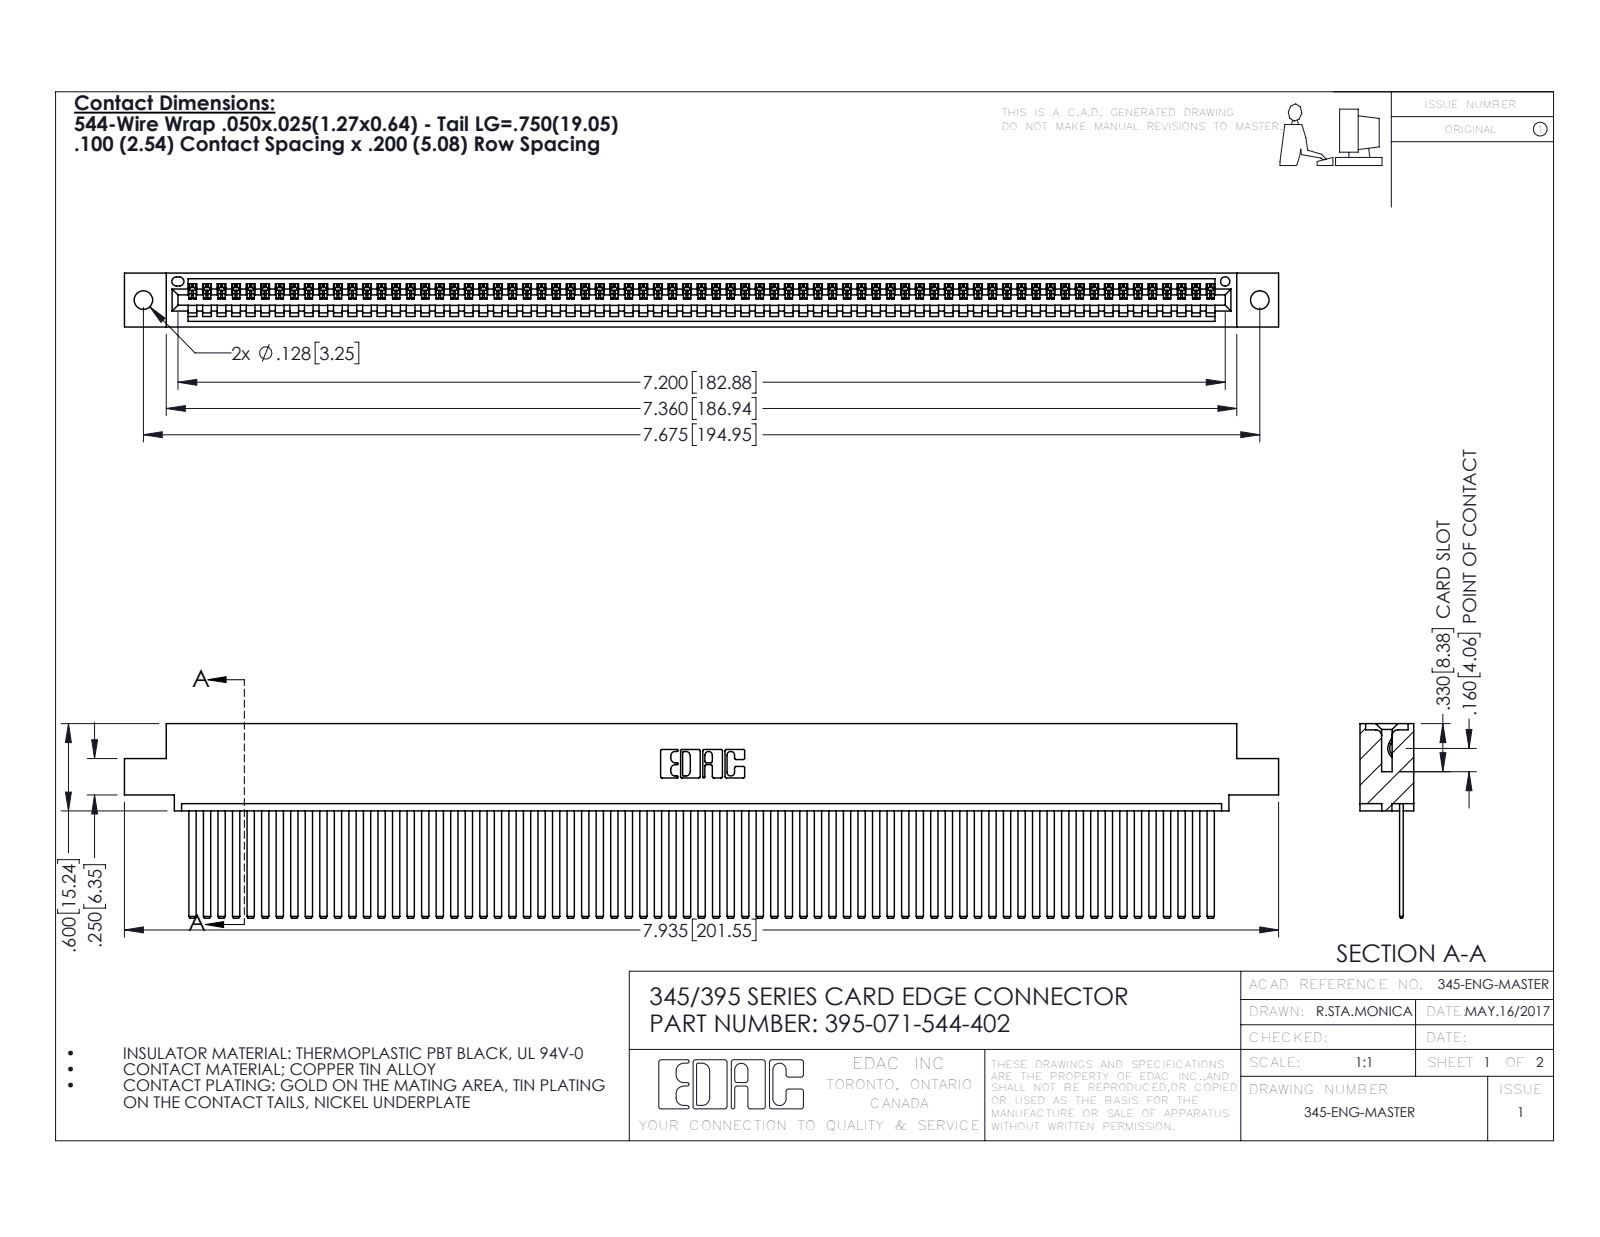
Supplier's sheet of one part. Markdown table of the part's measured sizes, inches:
| quantity | value |
| --- | --- |
| part name | 395-071-544-402; 345-292-001_345-293-144; 345 Part_0.110 Offset - 0.128 Dia |
| STEP written by | SolidWorks 2016 (CONFIG_CONTROL_DESIGN) |
| units | inches |
| bodies | 72 solids, 3822 faces (2640 planar, 1182 cylindrical, 0 other) |
| overall size | 7.935 × 1.337 × 0.37 |
| volume | 1.226 in³ |
| surface area | 45.53 in² |
| round holes (diameter × count) | 0.128 × 2, 0.064 × 1 |
| partial cylindrical surfaces (radius × count) | 0.006 × 142, 0.01 × 22, 0.007 × 6, 0.031 × 6, 0.026 × 3, 0.031 × 2, 0.04 × 2, 0.014 × 1 |
| main face-to-face distances | 0.072, 0.298, 0.025, 0.098, 0.272, 0.37, 0.2, 0.225, 0.149, 0.072 |
| hole center spacings | 0.27, 7.439, 7.675 |
